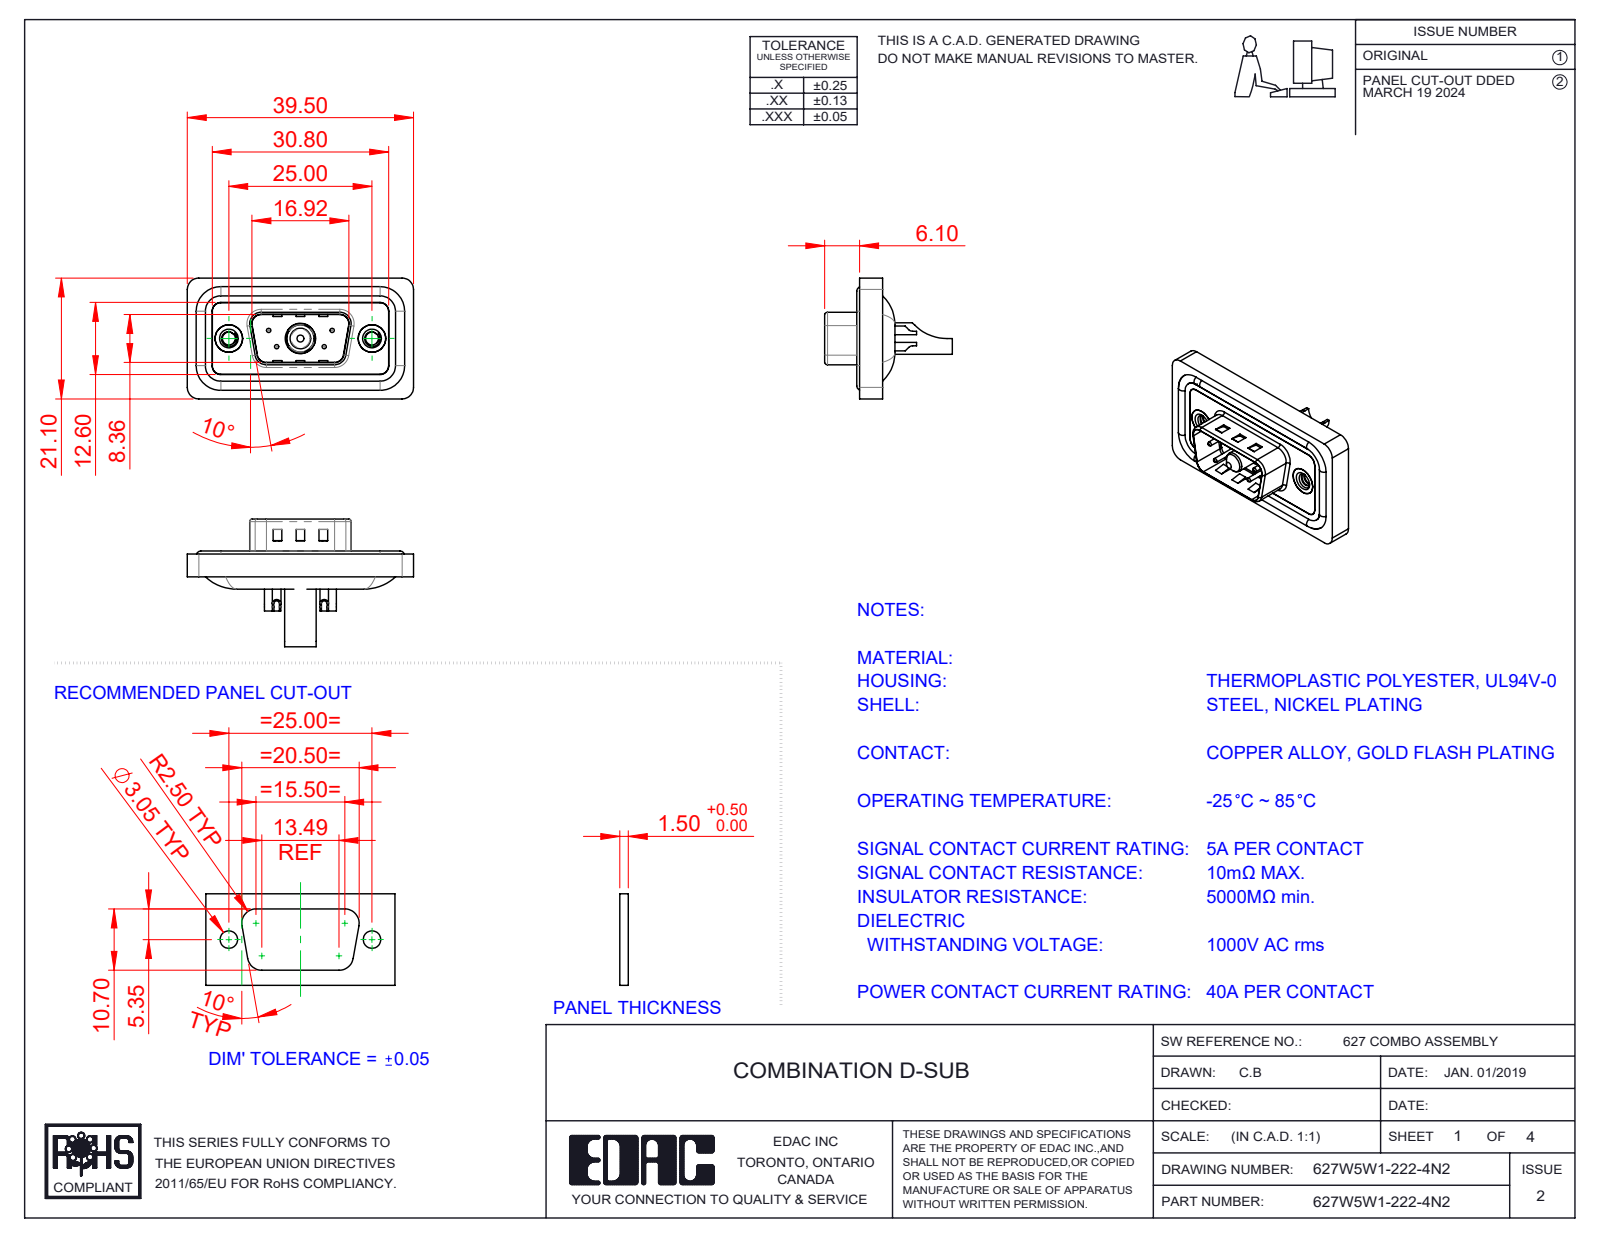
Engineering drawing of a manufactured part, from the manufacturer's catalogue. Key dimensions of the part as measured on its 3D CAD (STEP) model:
Part name (STEP PRODUCT): 627Combo Housing_5W1; 627Combo Contact Row 2_22; 627Combo Threaded Rivet_2; Power Pin_40A SC (+5 more)
STEP written by: SolidWorks 2023 (CONFIG_CONTROL_DESIGN)
Units: millimetres
Bodies: 13 solids, 602 faces (193 planar, 264 cylindrical, 145 other)
Overall size (bounding box): 39.5 × 22.3 × 21.1
Volume: 4 434 mm³ · Surface area: 7 113 mm²
Round holes (diameter × count): ⌀0.75 ×4, ⌀1 ×4, ⌀1.6 ×4, ⌀2 ×4, ⌀2.26 ×2, ⌀4 ×2, ⌀4.8 ×2, ⌀5 ×2, ⌀4.6 ×1, ⌀4.85 ×1, ⌀5.3 ×1
Round bosses / shafts (diameter × count): ⌀1.6 ×4, ⌀1.5 ×4, ⌀4.9 ×2, ⌀5.5 ×1, ⌀5.2 ×1, ⌀4.75 ×1, ⌀3.75 ×1, ⌀3.6 ×1
Partial cylindrical surfaces — rounded edges, fillets, slot ends (radius × count): R1.5 ×22, R2 ×18, R0.5 ×8, R1.6 ×8, R1 ×6, R0.25 ×4, R0.6 ×4, R0.65 ×4
Main face-to-face distances: 0.4, 1.1, 2.9, 1.6, 3.1, 0.5, 1.5, 2.5, 4, 0.8
Hole centre spacings: 3.16, 5.72, 7.1, 12.5, 18.1, 4.39, 4.4, 8.31
